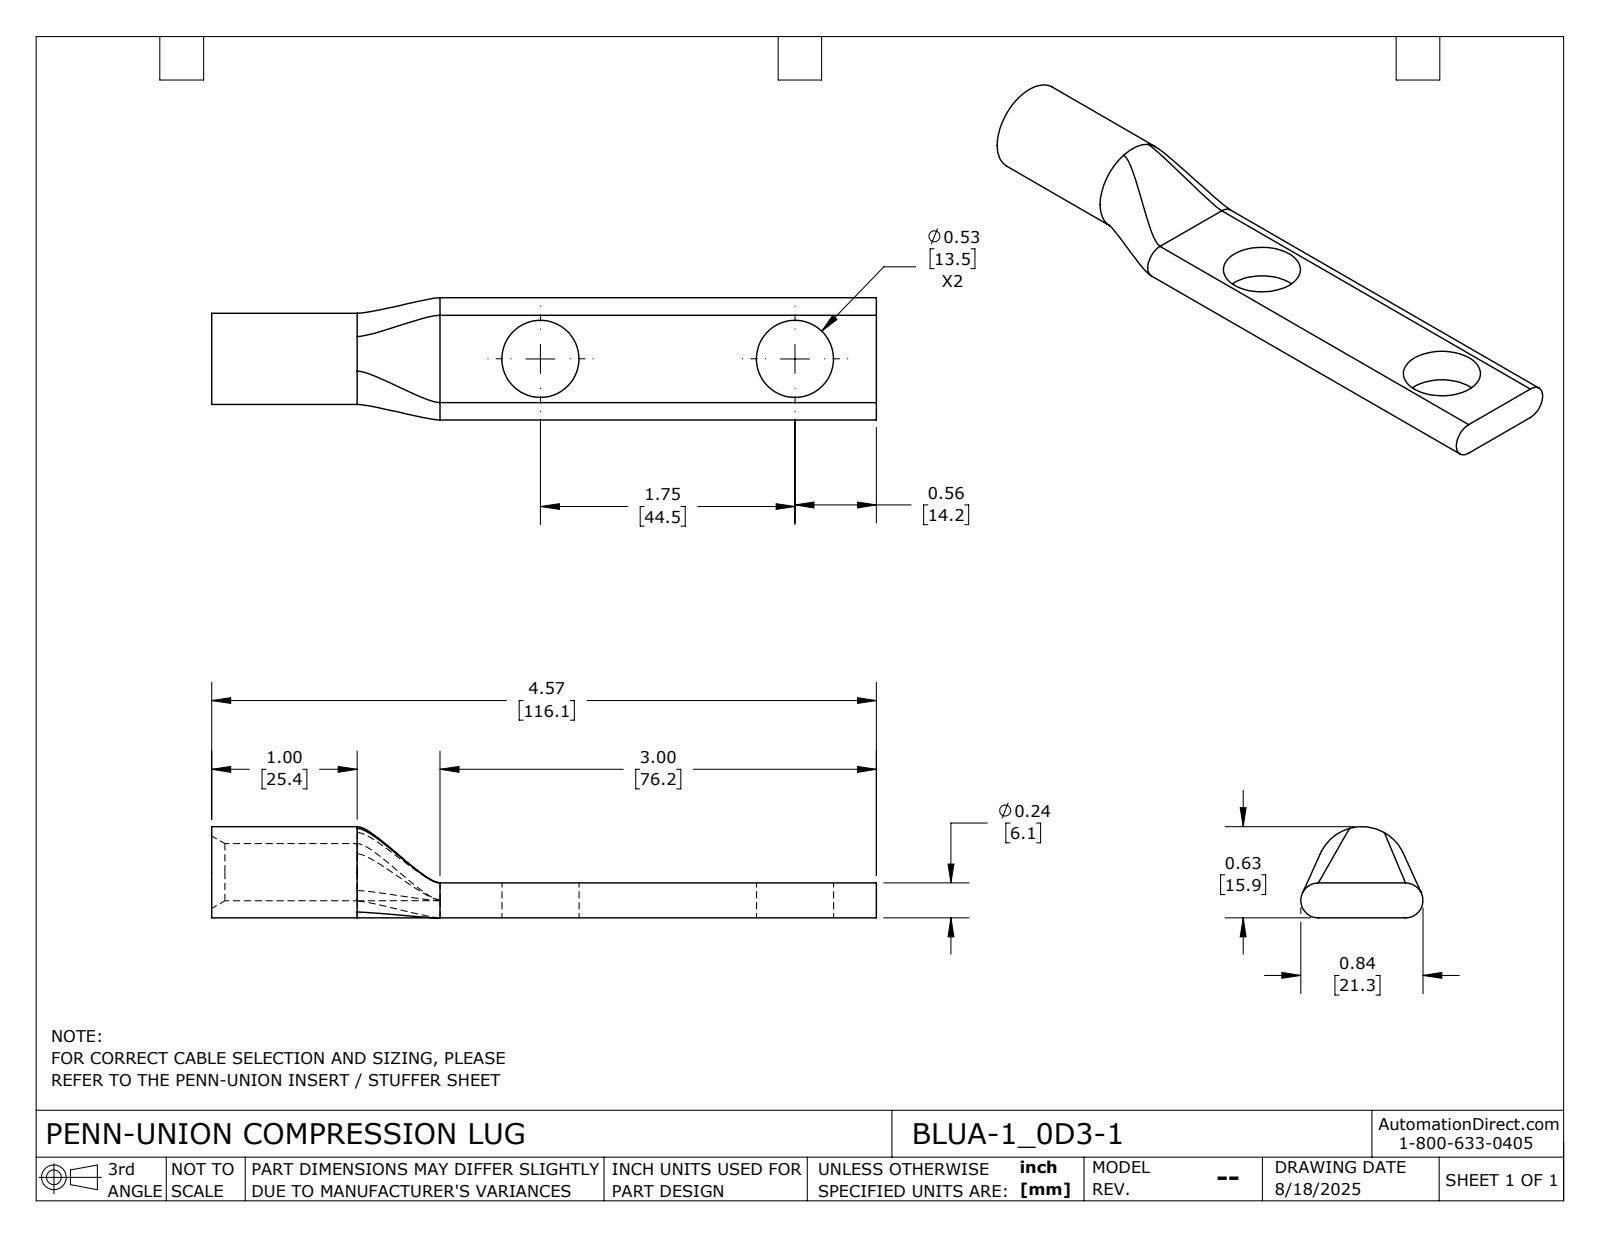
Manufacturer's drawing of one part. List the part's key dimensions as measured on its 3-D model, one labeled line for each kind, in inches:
Part name (STEP PRODUCT): BLUA-1_0D3-1
STEP written by: SolidWorks 2024 (CONFIG_CONTROL_DESIGN)
Units: inches
Bodies: 1 solid, 26 faces (5 planar, 11 cylindrical, 10 other)
Overall size (bounding box): 4.57 × 0.84 × 0.627
Volume: 0.752 in³ · Surface area: 11.24 in²
Round holes (diameter × count): ⌀0.53 ×2, ⌀0.393 ×1
Round bosses / shafts (diameter × count): ⌀0.627 ×1
Partial cylindrical surfaces — rounded edges, fillets, slot ends (radius × count): R0.12 ×2
Main face-to-face distances: 0.24, 4.57, 1.57, 3
Hole centre spacings: 1.75
